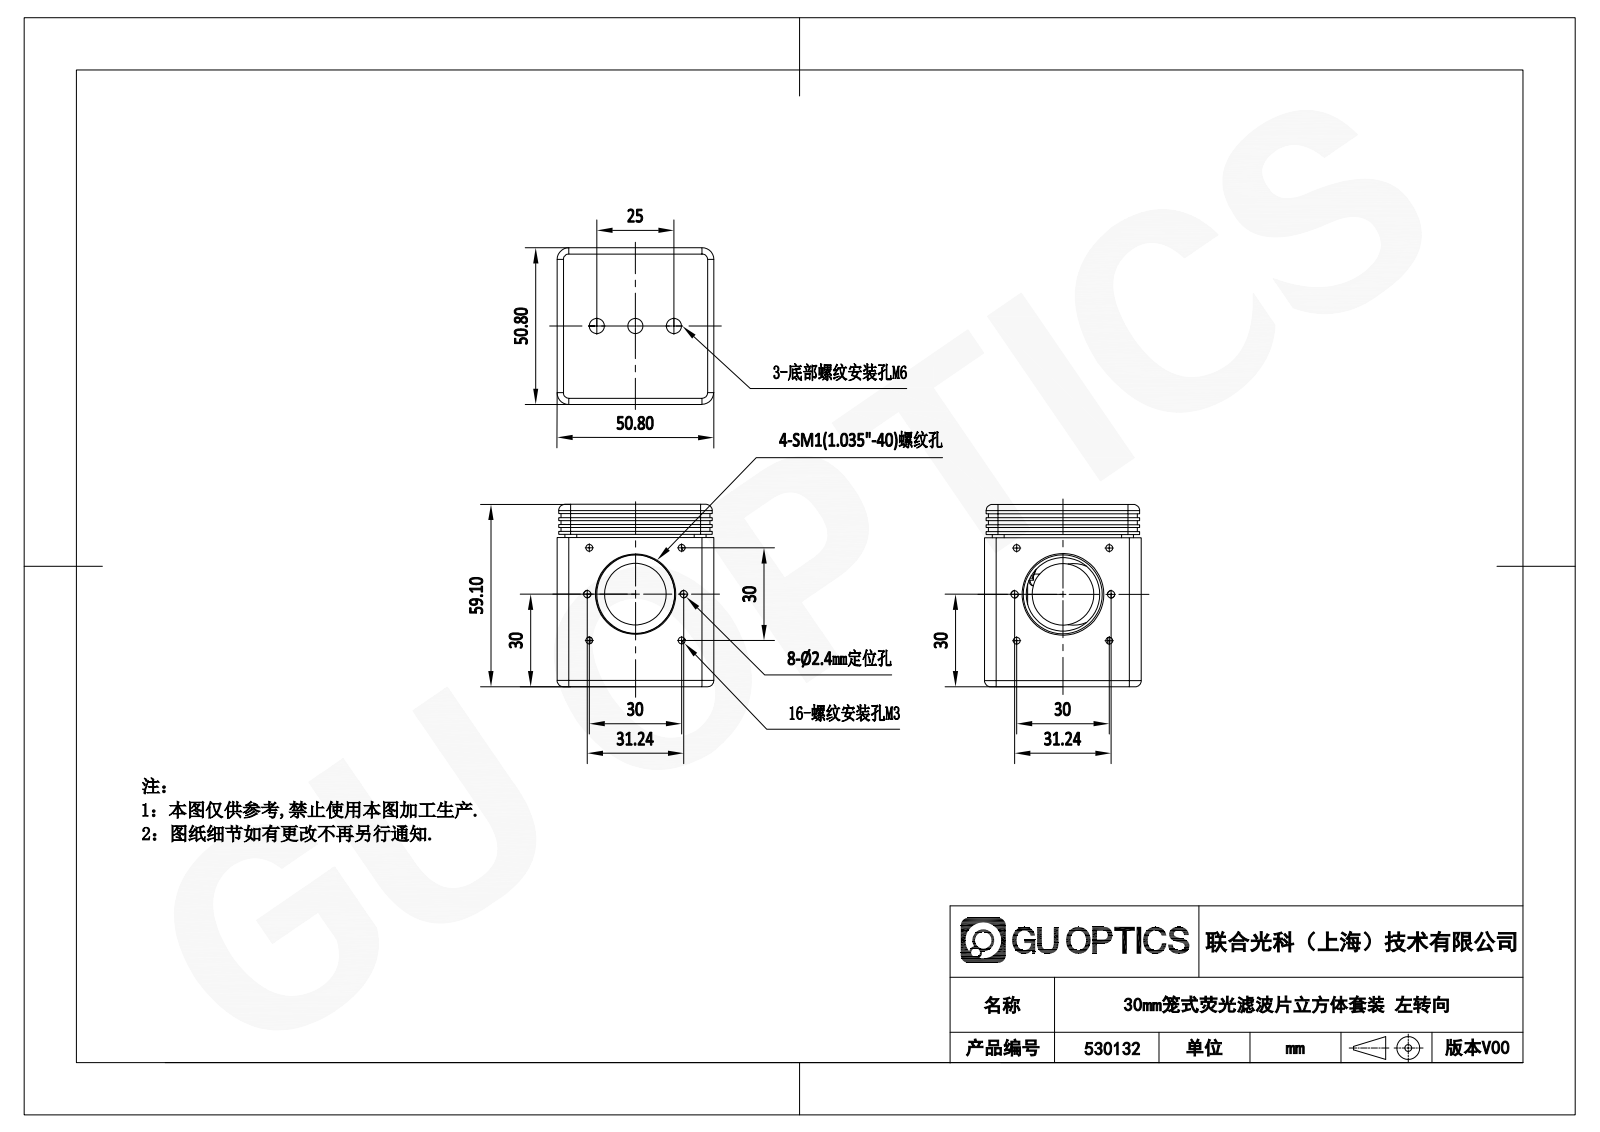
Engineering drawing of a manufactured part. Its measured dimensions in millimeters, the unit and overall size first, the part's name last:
Units: millimetres
Overall size (bounding box): 59.12 × 50.8 × 50.8
Round holes (diameter × count): ⌀2.5 ×11, ⌀5 ×6, ⌀2.41 ×4, ⌀5.08 ×4, ⌀25.6 ×4, ⌀4 ×3, ⌀1.6 ×2, ⌀2.03 ×2, ⌀2.05 ×2, ⌀2.9 ×2, ⌀3.4 ×2, ⌀5.6 ×2
Round bosses / shafts (diameter × count): ⌀1.5 ×6, ⌀5.5 ×2, ⌀4.6 ×2, ⌀3 ×2, ⌀2.5 ×2, ⌀2 ×2
Partial cylindrical surfaces — rounded edges, fillets, slot ends (radius × count): R3.3 ×20, R3.81 ×16, R3.43 ×14, R0.79 ×12, R3.17 ×9, R6.35 ×9, R2.03 ×8, R3.43 ×7
Main face-to-face distances: 3.81, 46.99, 1.27, 50.8, 2.54, 59.12, 0.63, 4.44, 46.36, 43.18
Hole centre spacings: 15.01, 21.21, 30, 34.1, 33, 36.41, 14.51, 15.62
Volume: 81 487 mm³ · Surface area: 52 346 mm²
Bodies: 24 solids, 874 faces (466 planar, 262 cylindrical, 146 other)
Part name (STEP PRODUCT): 530132
STEP written by: SolidWorks 2020 (CONFIG_CONTROL_DESIGN)
